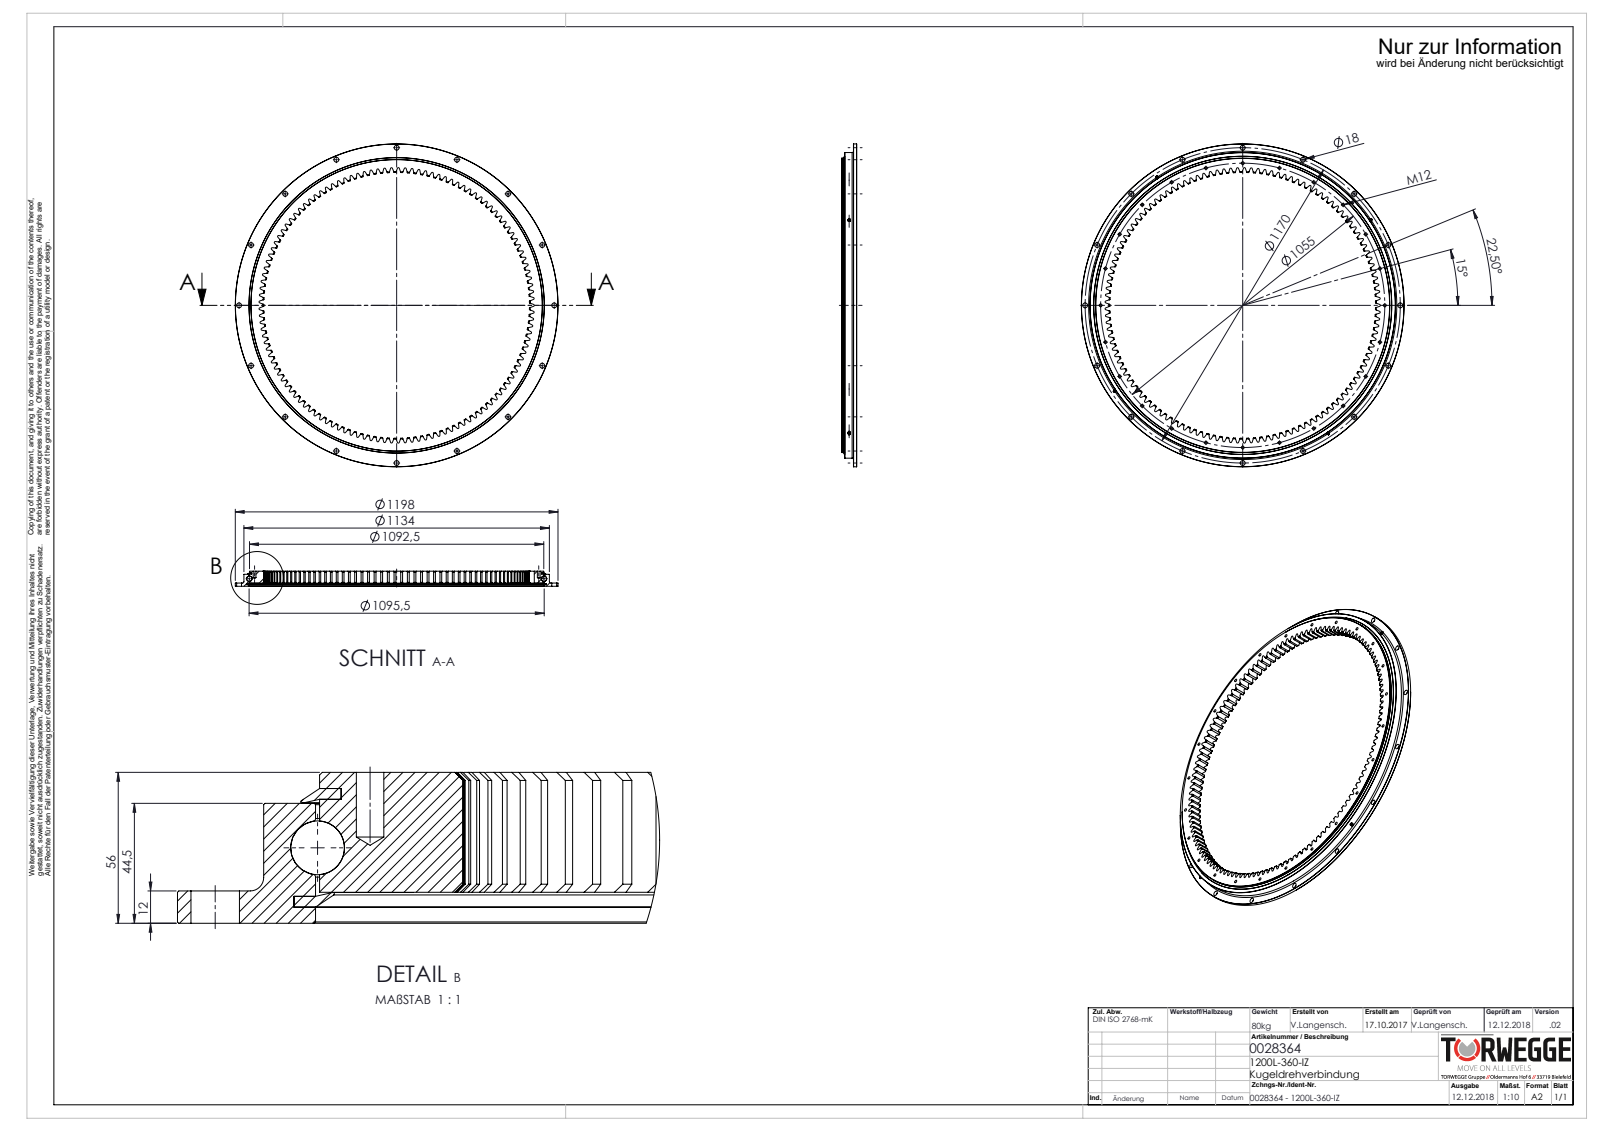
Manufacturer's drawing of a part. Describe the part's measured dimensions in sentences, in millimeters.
The part is named "0028364_1200L-360-IZ_(-03)". Its 3-D file was written by "SolidWorks 2018 (AUTOMOTIVE_DESIGN)". It is 12 solids with 927 faces: 61 planar, 277 cylindrical and 589 other. Overall it measures 1198 by 1198 by 56 millimeters. Its volume is 11 630 000 cubic millimeters and its surface area 1 839 000 square millimeters. Round holes: 24 of diameter 10.2, 16 of diameter 18, 4 of diameter 1.5, 4 of diameter 2, 4 of diameter 4.5, 4 of diameter 7, 1 of diameter 1076.5, 1 of diameter 1095.5, 1 of diameter 1111.5. Round bosses or shafts: 4 of diameter 8, 4 of diameter 4, 1 of diameter 1198, 1 of diameter 1134, 1 of diameter 1092.5. Partial cylindrical surfaces (rounded edges, fillets, slot ends): 1 of radius 493. The main face-to-face distances are 11.5, 44.5, 6, 44, 56, 5.5, 10, 46, 1.5, 34.5. The hole center spacings are 527.5, 228.26, 447.74, 585, 650.02, 972.82, 1080.94, 1147.52.
